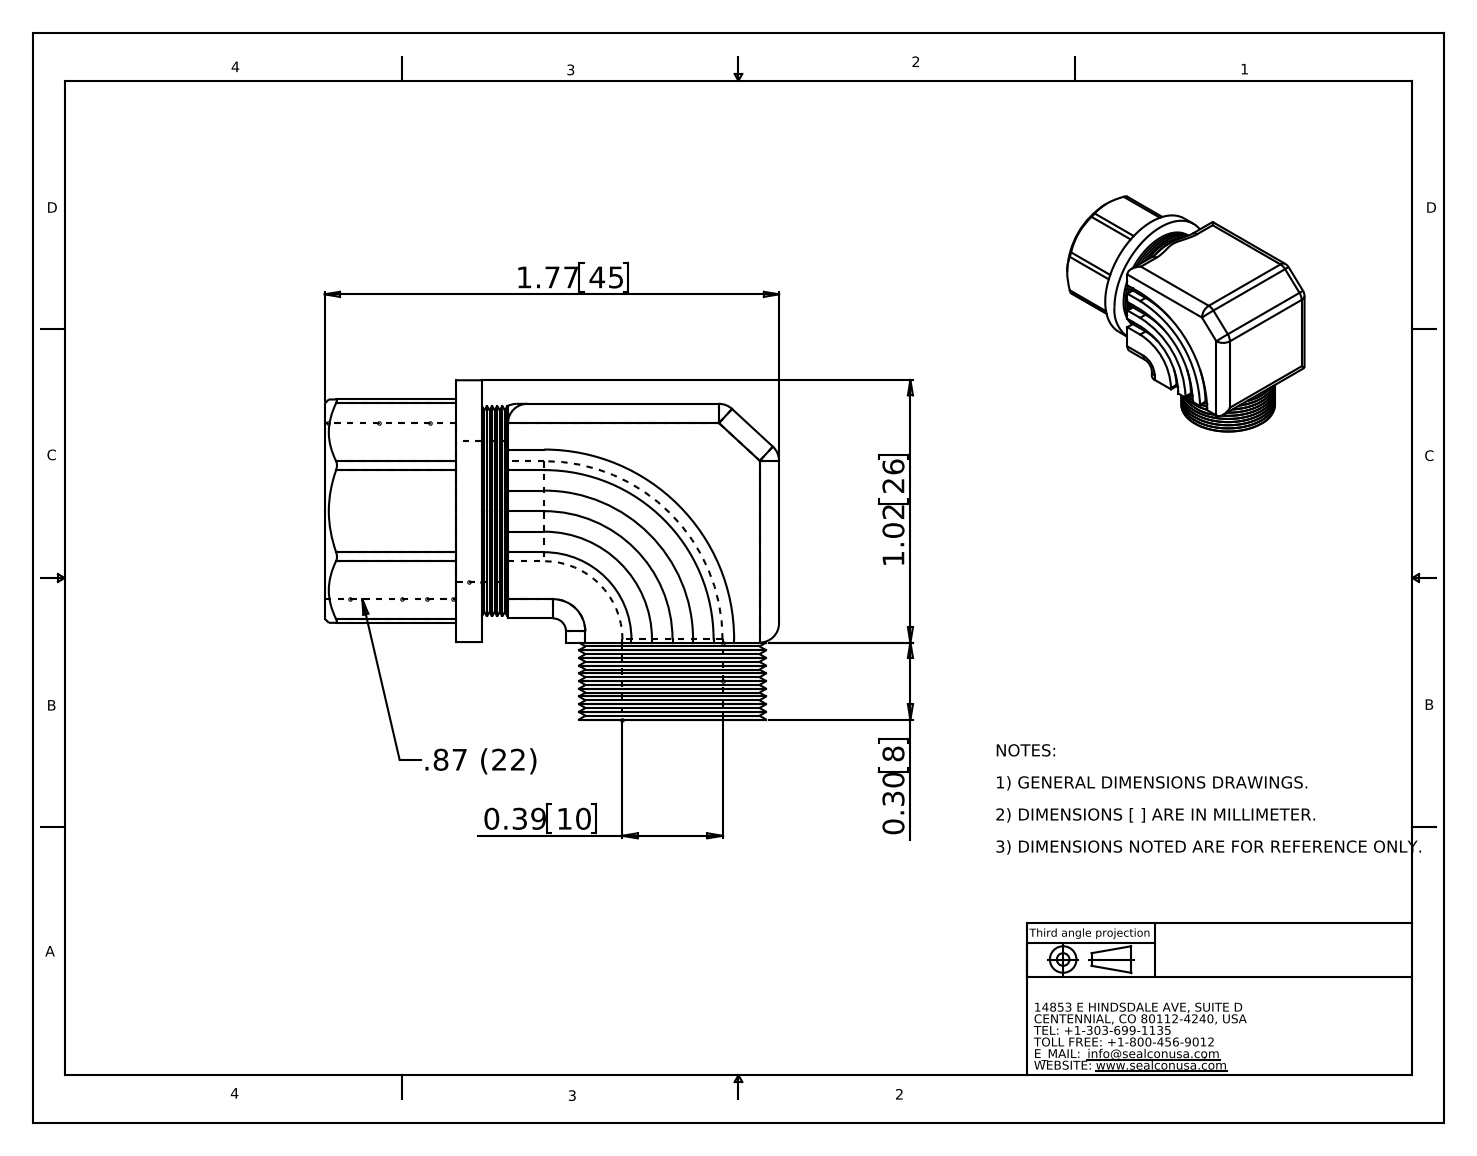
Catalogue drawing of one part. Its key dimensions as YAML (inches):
part_name: "ET09AA-BK"
step_written_by: "SolidWorks 2008 (CONFIG_CONTROL_DESIGN)"
units: inches
bodies: {solids: 3, faces: 206, planar: 63, cylindrical: 52, other: 91}
overall_size: [1.77, 1.322, 1.02]
volume: 1.034
surface_area: 14.01
round_holes:
  - {diameter: 0.39, count: 2}
  - {diameter: 0.55, count: 1}
  - {diameter: 0.687, count: 1}
round_bosses_or_shafts:
  - {diameter: 1.02, count: 1}
  - {diameter: 0.82, count: 1}
partial_cylinders:
  - {radius: 0.075, count: 14}
  - {radius: 0.05, count: 9}
  - {radius: 0.34, count: 1}
  - {radius: 0.42, count: 1}
  - {radius: 0.5, count: 1}
  - {radius: 0.58, count: 1}
  - {radius: 0.66, count: 1}
  - {radius: 0.74, count: 1}
face_to_face_distances: [0.87, 0.93, 0.94, 1.158, 0.06, 0.88, 0.035, 0.905, 0.025, 0.845]
